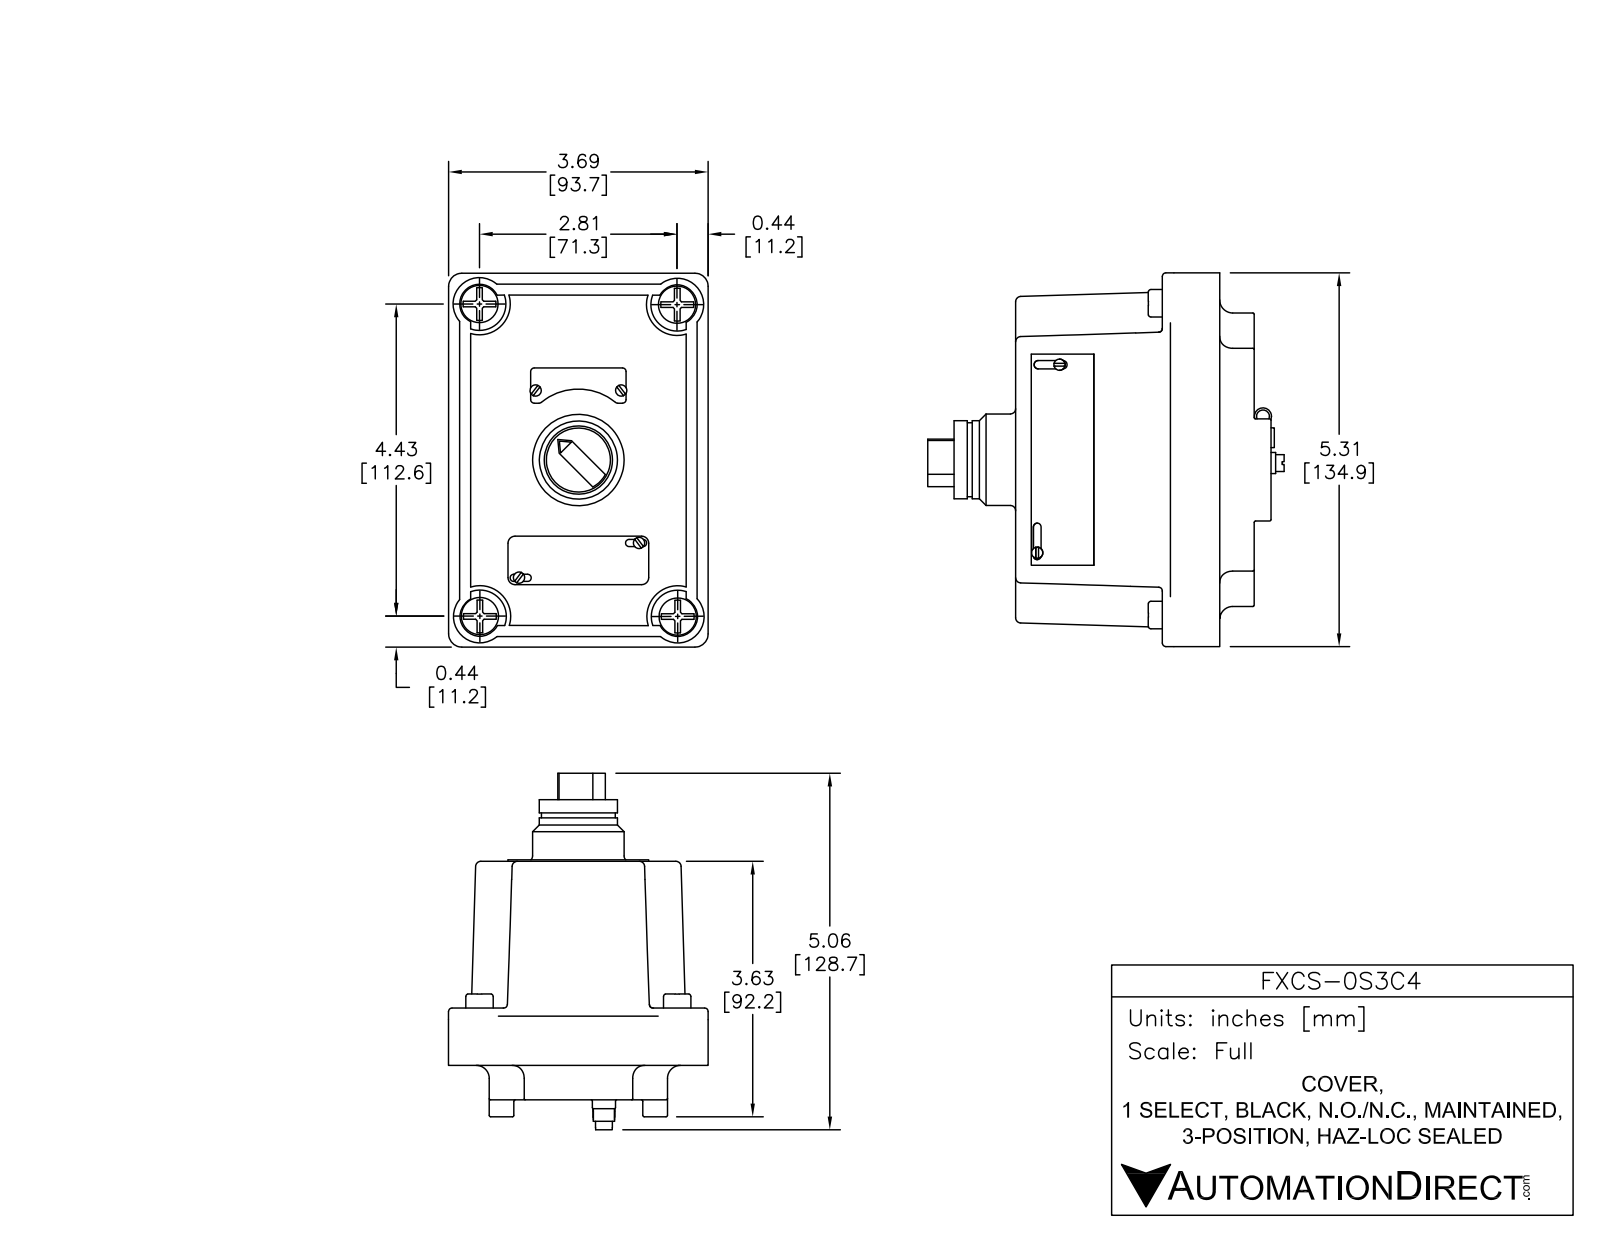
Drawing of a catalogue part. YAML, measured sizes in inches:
part_name: "FXCS-0S3C4"
step_written_by: "SolidWorks 2015 (AUTOMOTIVE_DESIGN)"
units: inches
bodies: {solids: 2, faces: 710, planar: 308, cylindrical: 166, other: 236}
overall_size: [5.31, 5.066, 3.69]
volume: 48.91
surface_area: 100.9
round_holes:
  - {diameter: 0.16, count: 8}
  - {diameter: 0.198, count: 1}
  - {diameter: 0.97, count: 1}
round_bosses_or_shafts:
  - {diameter: 0.16, count: 8}
  - {diameter: 0.39, count: 4}
  - {diameter: 1.3, count: 1}
  - {diameter: 1.11, count: 1}
  - {diameter: 1.05, count: 1}
  - {diameter: 0.91, count: 1}
  - {diameter: 0.33, count: 1}
  - {diameter: 0.3, count: 1}
partial_cylinders:
  - {radius: 0.05, count: 24}
  - {radius: 0.02, count: 22}
  - {radius: 0.051, count: 4}
  - {radius: 0.055, count: 4}
  - {radius: 0.06, count: 4}
  - {radius: 0.075, count: 4}
  - {radius: 0.1, count: 4}
  - {radius: 0.185, count: 4}
face_to_face_distances: [3.39, 0.49, 2.9, 0.021, 3.69, 0.578, 3.111, 1.19, 0.7, 2.2]
hole_center_spacings: [0.25, 2.197, 0.5, 2.183, 2.239, 0.75, 1.092, 1.115]
